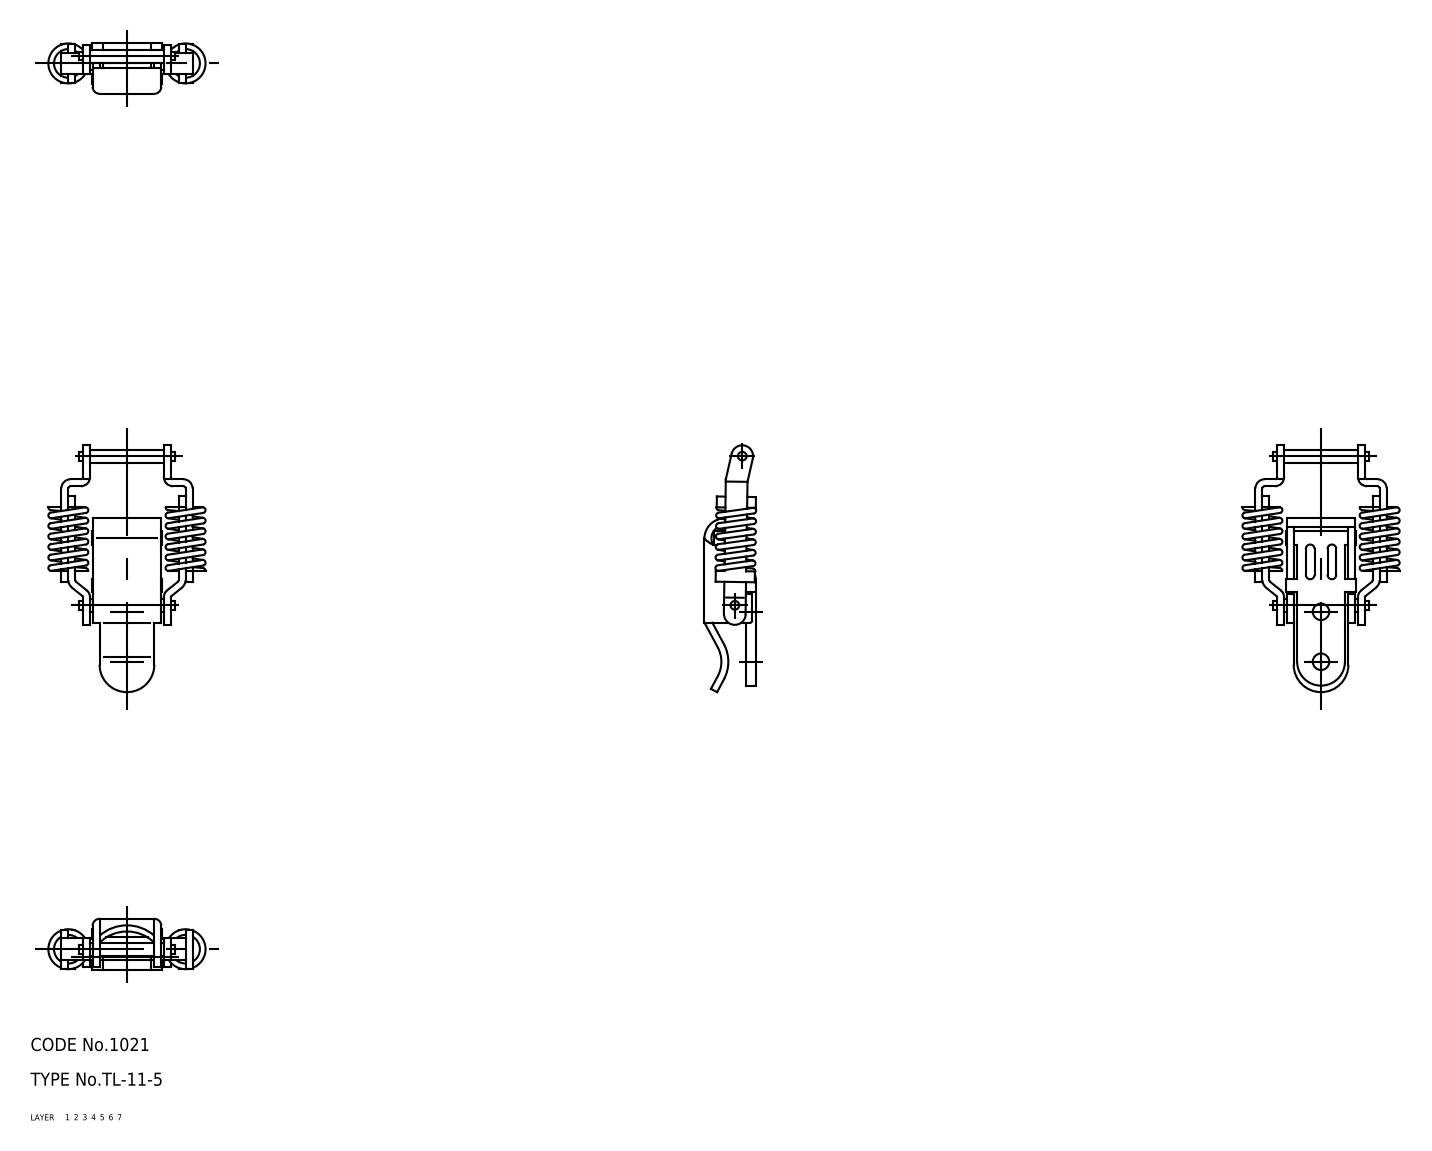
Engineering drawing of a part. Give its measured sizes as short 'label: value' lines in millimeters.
name: arm_C_mr; arm_C; arm_B; arm_A (+5 more)
written by: CADfix (AUTOMOTIVE_DESIGN)
unit: mm
bodies: 10 solids, 261 faces (0 planar, 0 cylindrical, 261 other)
size: 56.85 × 37 × 11.8
volume: 4 238 mm³; area: 7 013 mm²
